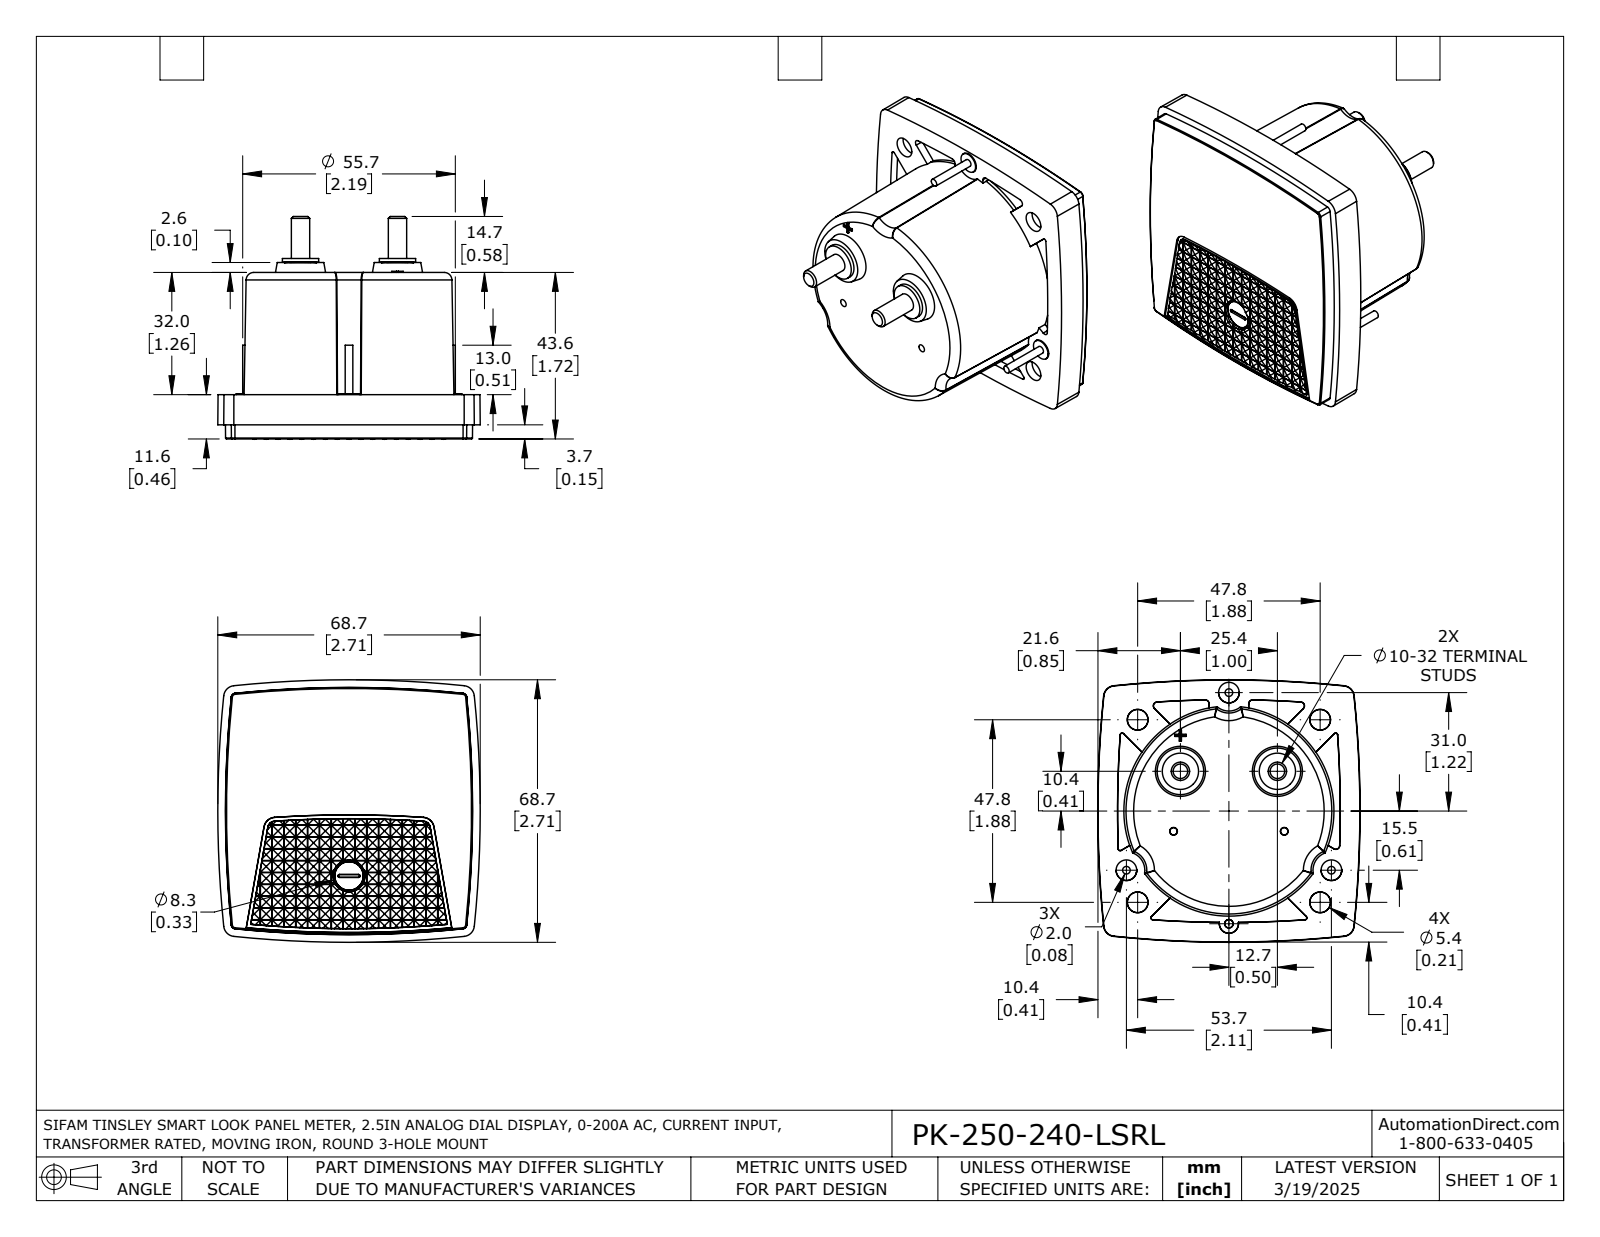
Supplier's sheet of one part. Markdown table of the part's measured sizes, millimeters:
| quantity | value |
| --- | --- |
| part name | PK-250-240-LSRL |
| STEP written by | SolidWorks 2021 (AUTOMOTIVE_DESIGN) |
| units | millimeters |
| bodies | 1 solid, 1550 faces (1165 planar, 265 cylindrical, 120 other) |
| overall size | 68.7 × 68.7 × 58.3 |
| volume | 124 400 mm³ |
| surface area | 19 620 mm² |
| round bosses / shafts (diameter × count) | 5.4 × 3, 2 × 3, 9.5 × 2, 4.8 × 2, 5.5 × 1 |
| partial cylindrical surfaces (radius × count) | 4.2 × 2, 27.5 × 1 |
| main face-to-face distances | 43.6, 32, 11.6, 0.6, 2.2, 2.4, 7.9, 3, 1.8, 34.2 |
